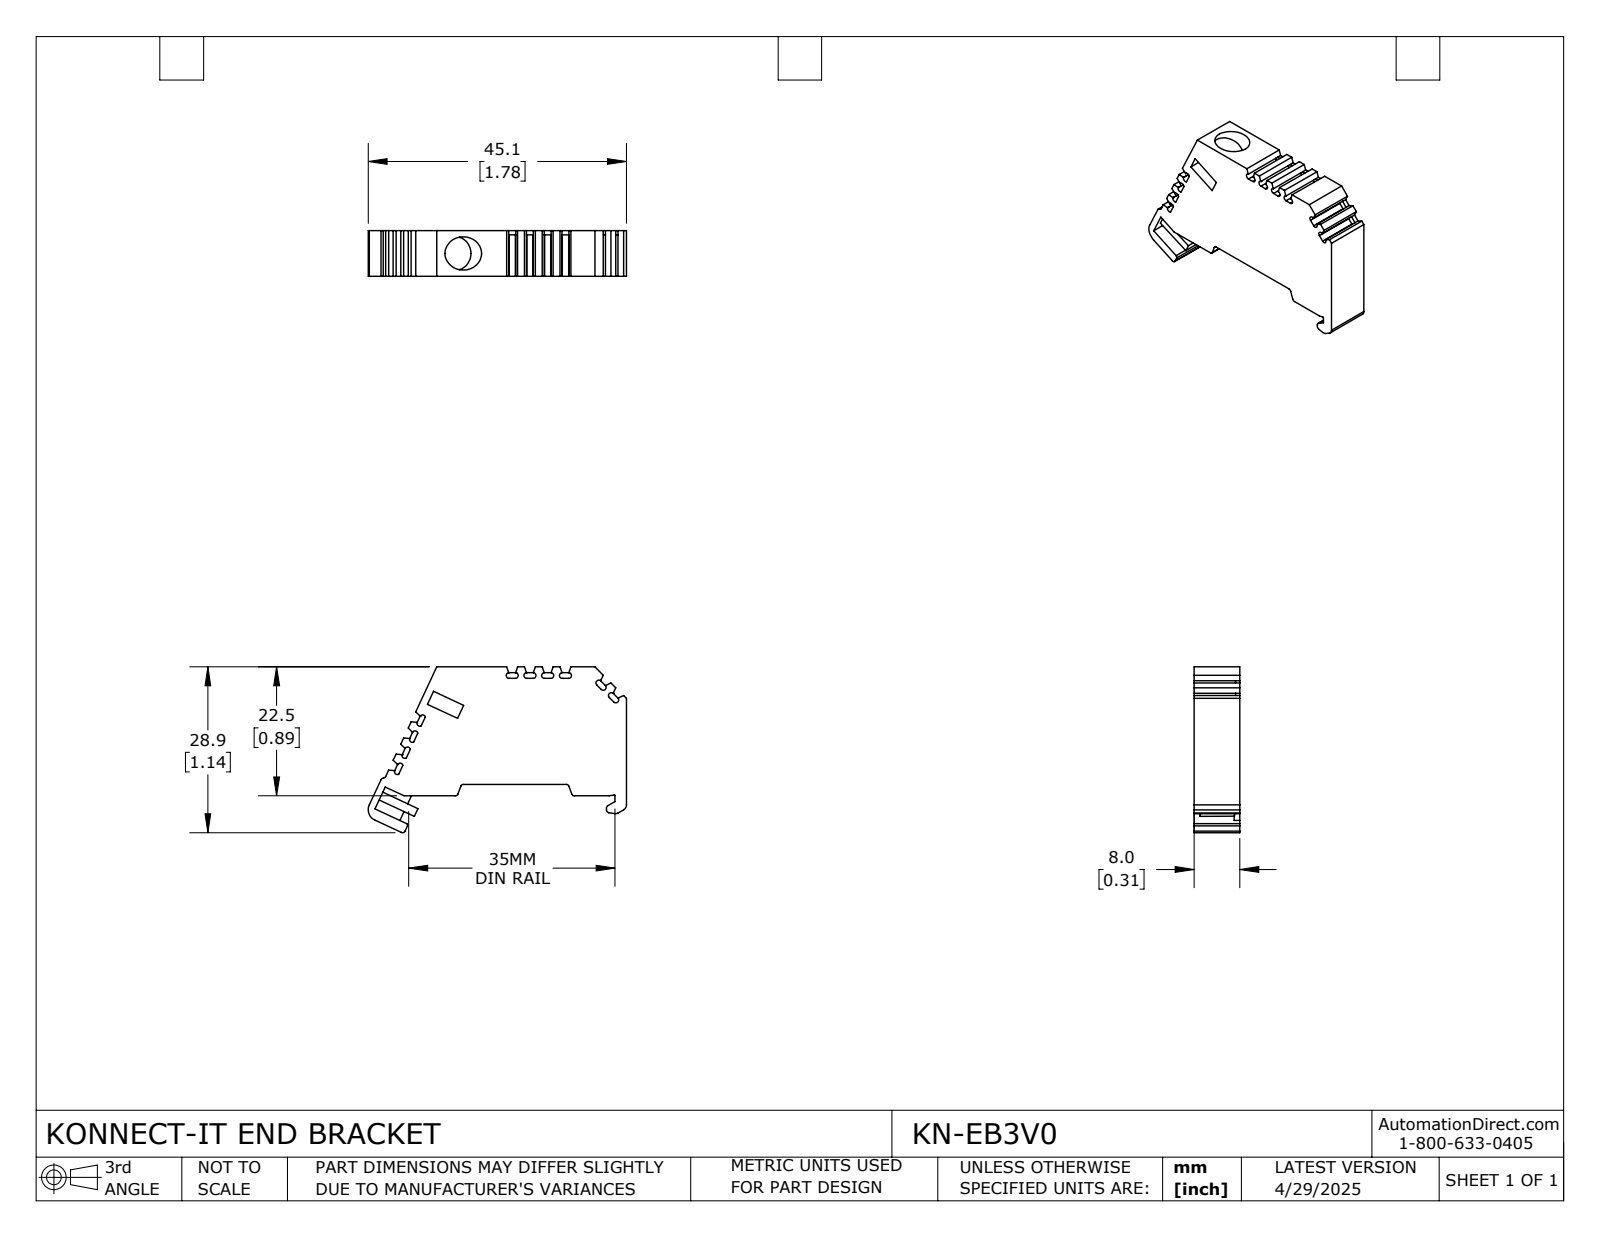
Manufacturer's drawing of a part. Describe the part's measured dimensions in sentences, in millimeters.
The part is named "KN-EB3V0". Its 3-D file was written by "SolidWorks 2024 (CONFIG_CONTROL_DESIGN)". It is 1 solid with 161 faces: 116 planar, 45 cylindrical and 0 other. Overall it measures 45.09 by 28.94 by 8 millimeters. Its volume is 6 266 cubic millimeters and its surface area 3 463 square millimeters. Round holes: 1 of diameter 3, 1 of diameter 5.8. Partial cylindrical surfaces (rounded edges, fillets, slot ends): 29 of radius 0.5, 2 of radius 1, 1 of radius 0.1, 1 of radius 0.3, 1 of radius 2. The main face-to-face distances are 8, 2, 20.5, 22.5, 2.93, 2.5, 18.7, 1, 1.9, 20.4.
